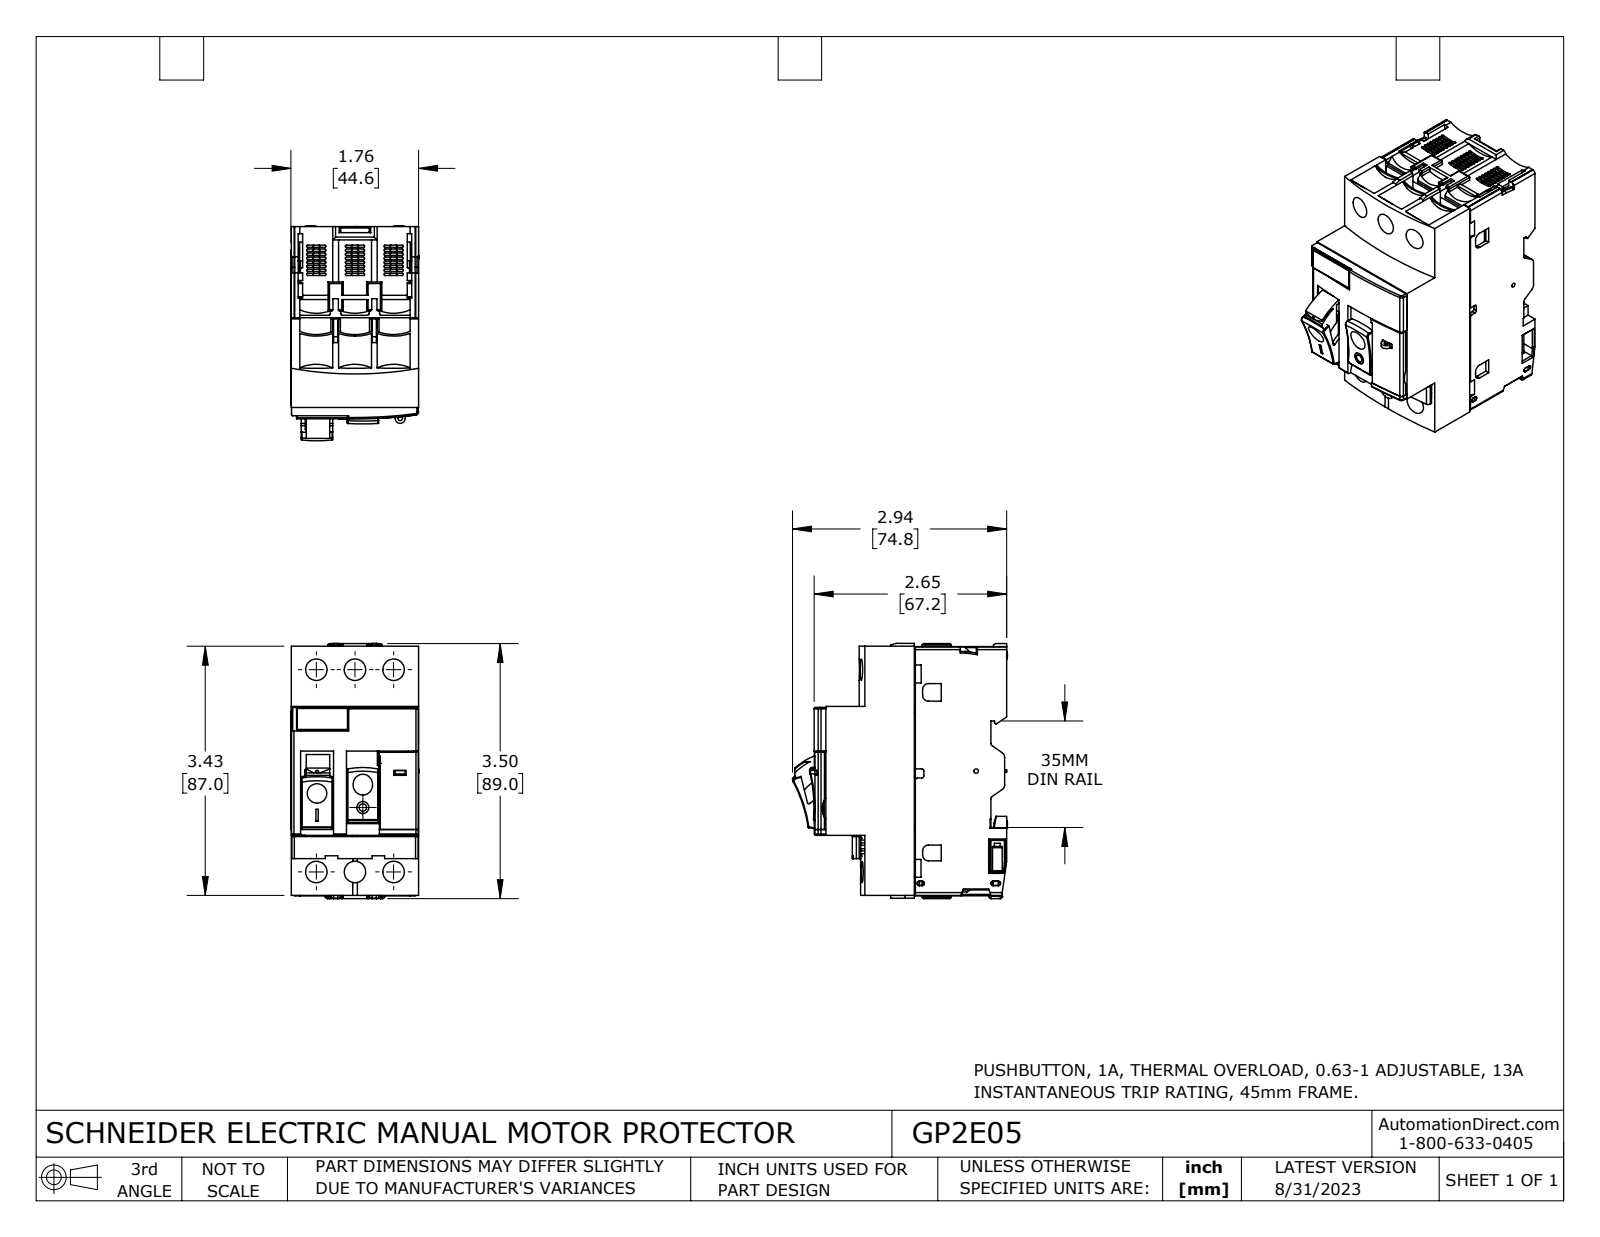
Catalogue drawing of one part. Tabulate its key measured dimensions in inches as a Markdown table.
| quantity | value |
| --- | --- |
| part name | GP2E05 |
| STEP written by | SolidWorks 2021 (CONFIG_CONTROL_DESIGN) |
| units | inches |
| bodies | 15 solids, 2269 faces (1521 planar, 657 cylindrical, 91 other) |
| overall size | 3.508 × 2.957 × 1.764 |
| volume | 11.58 in³ |
| surface area | 98.93 in² |
| round holes (diameter × count) | 0.295 × 6, 0.197 × 5, 0.059 × 2, 0.157 × 1, 0.165 × 1, 0.315 × 1, 0.327 × 1, 0.335 × 1, 0.343 × 1 |
| round bosses / shafts (diameter × count) | 0.244 × 2, 0.118 × 2, 0.382 × 1, 0.102 × 1, 0.047 × 1 |
| partial cylindrical surfaces (radius × count) | 0.016 × 104, 0.02 × 47, 0.039 × 16, 0.01 × 12, 0.012 × 12, 0.031 × 12, 0.059 × 8, 0.004 × 6 |
| main face-to-face distances | 1.752, 0.531, 0.115, 1.233, 1.756, 0.059, 1.637, 0.581, 1.053, 1.171 |
| hole center spacings | 0.531, 2.83, 2.779, 0.346, 0.402, 0.546, 0.671, 0.726 |
